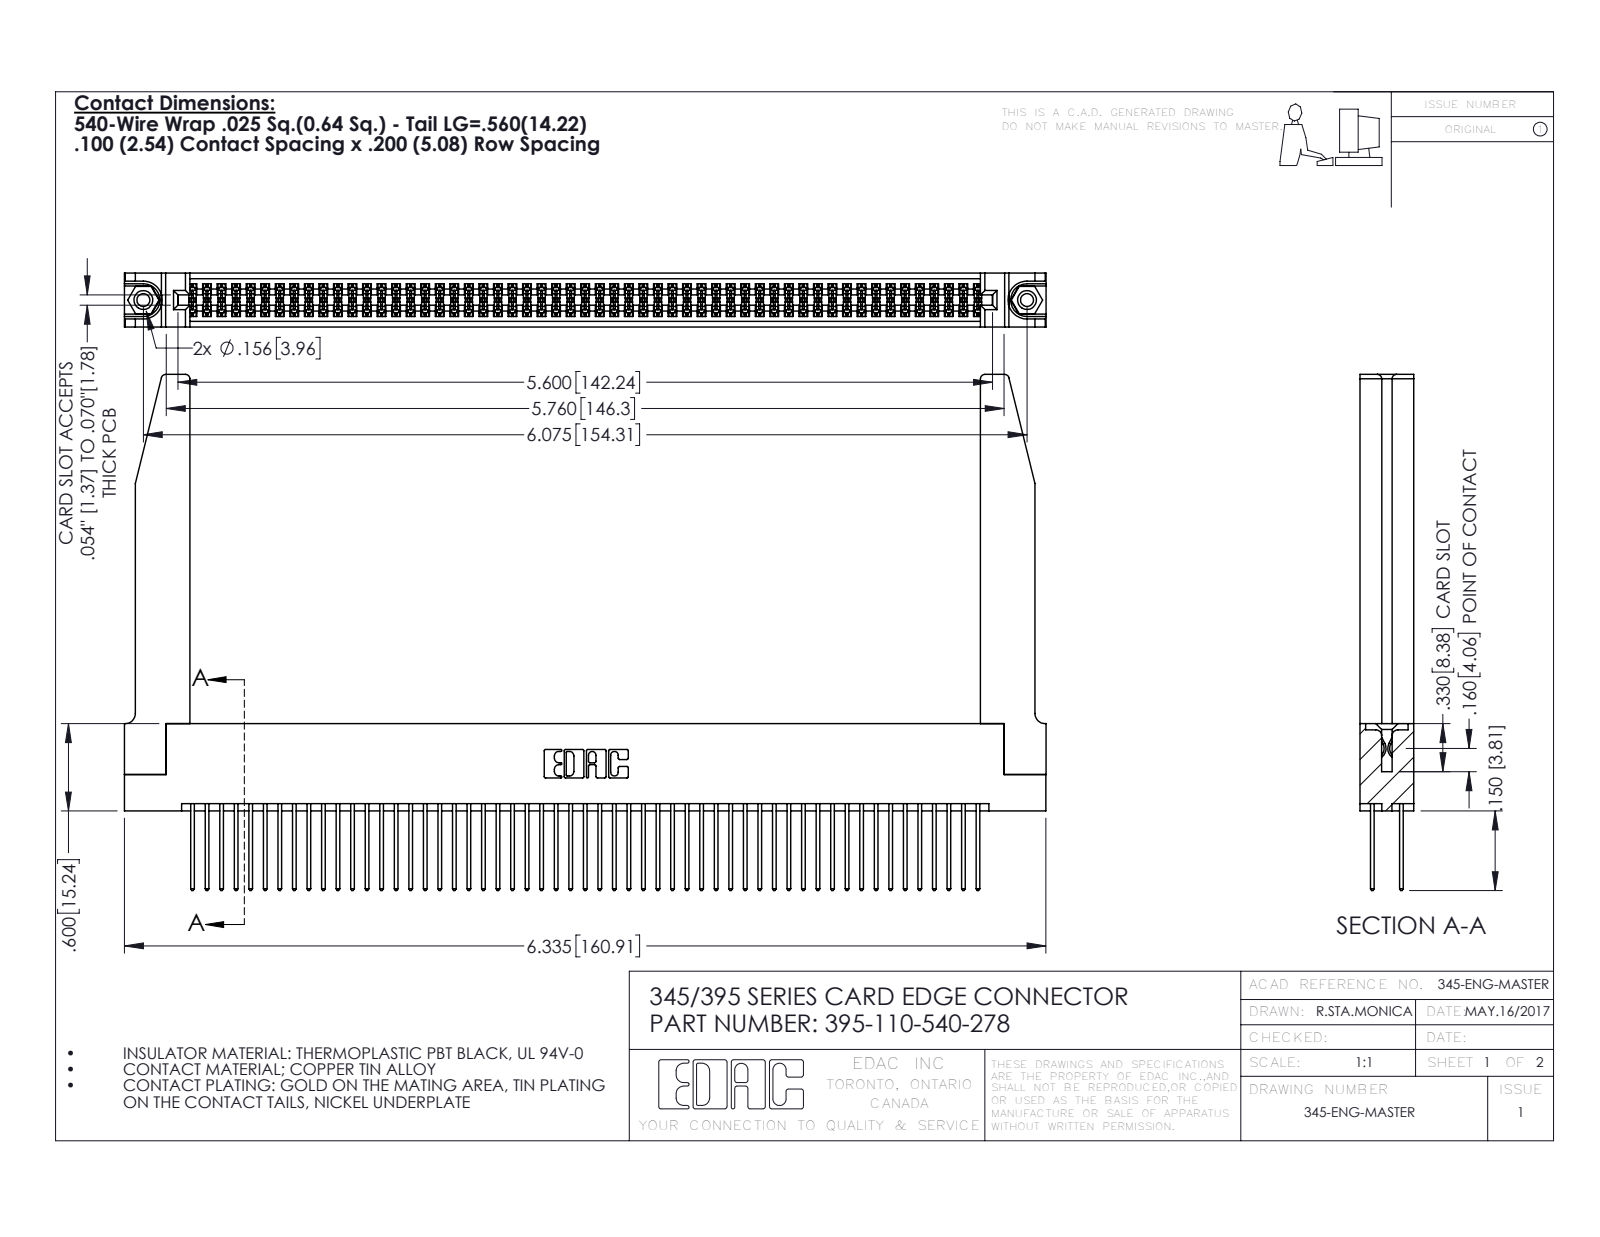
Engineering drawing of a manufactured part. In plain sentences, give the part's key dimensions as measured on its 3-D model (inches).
The part is named "345-220-078_345-220-078; 395-110-540-278; 345-250-001_345-250-001-102; 345-292-001_345-293-140 (+1 more)". Its 3-D file was written by "SolidWorks 2016 (CONFIG_CONTROL_DESIGN)". It is 115 solids with 5860 faces: 3852 planar, 1956 cylindrical and 52 other. Overall it measures 6.336 by 3.547 by 0.37 inches. Its volume is 1.461 cubic inches and its surface area 51.04 square inches. Round holes: 2 of diameter 0.089, 2 of diameter 0.125, 2 of diameter 0.156, 1 of diameter 0.064. Round bosses or shafts: 2 of diameter 0.155. Partial cylindrical surfaces (rounded edges, fillets, slot ends): 165 of radius 0.006, 110 of radius 0.01, 22 of radius 0.01, 8 of radius 0.03, 6 of radius 0.007, 6 of radius 0.031, 3 of radius 0.026, 2 of radius 0.014. The main face-to-face distances are 0.072, 0.298, 0.37, 0.2, 0.098, 0.272, 0.025, 0.225, 0.175, 0.148. The hole center spacings are 0.27, 5.839, 6.075.
